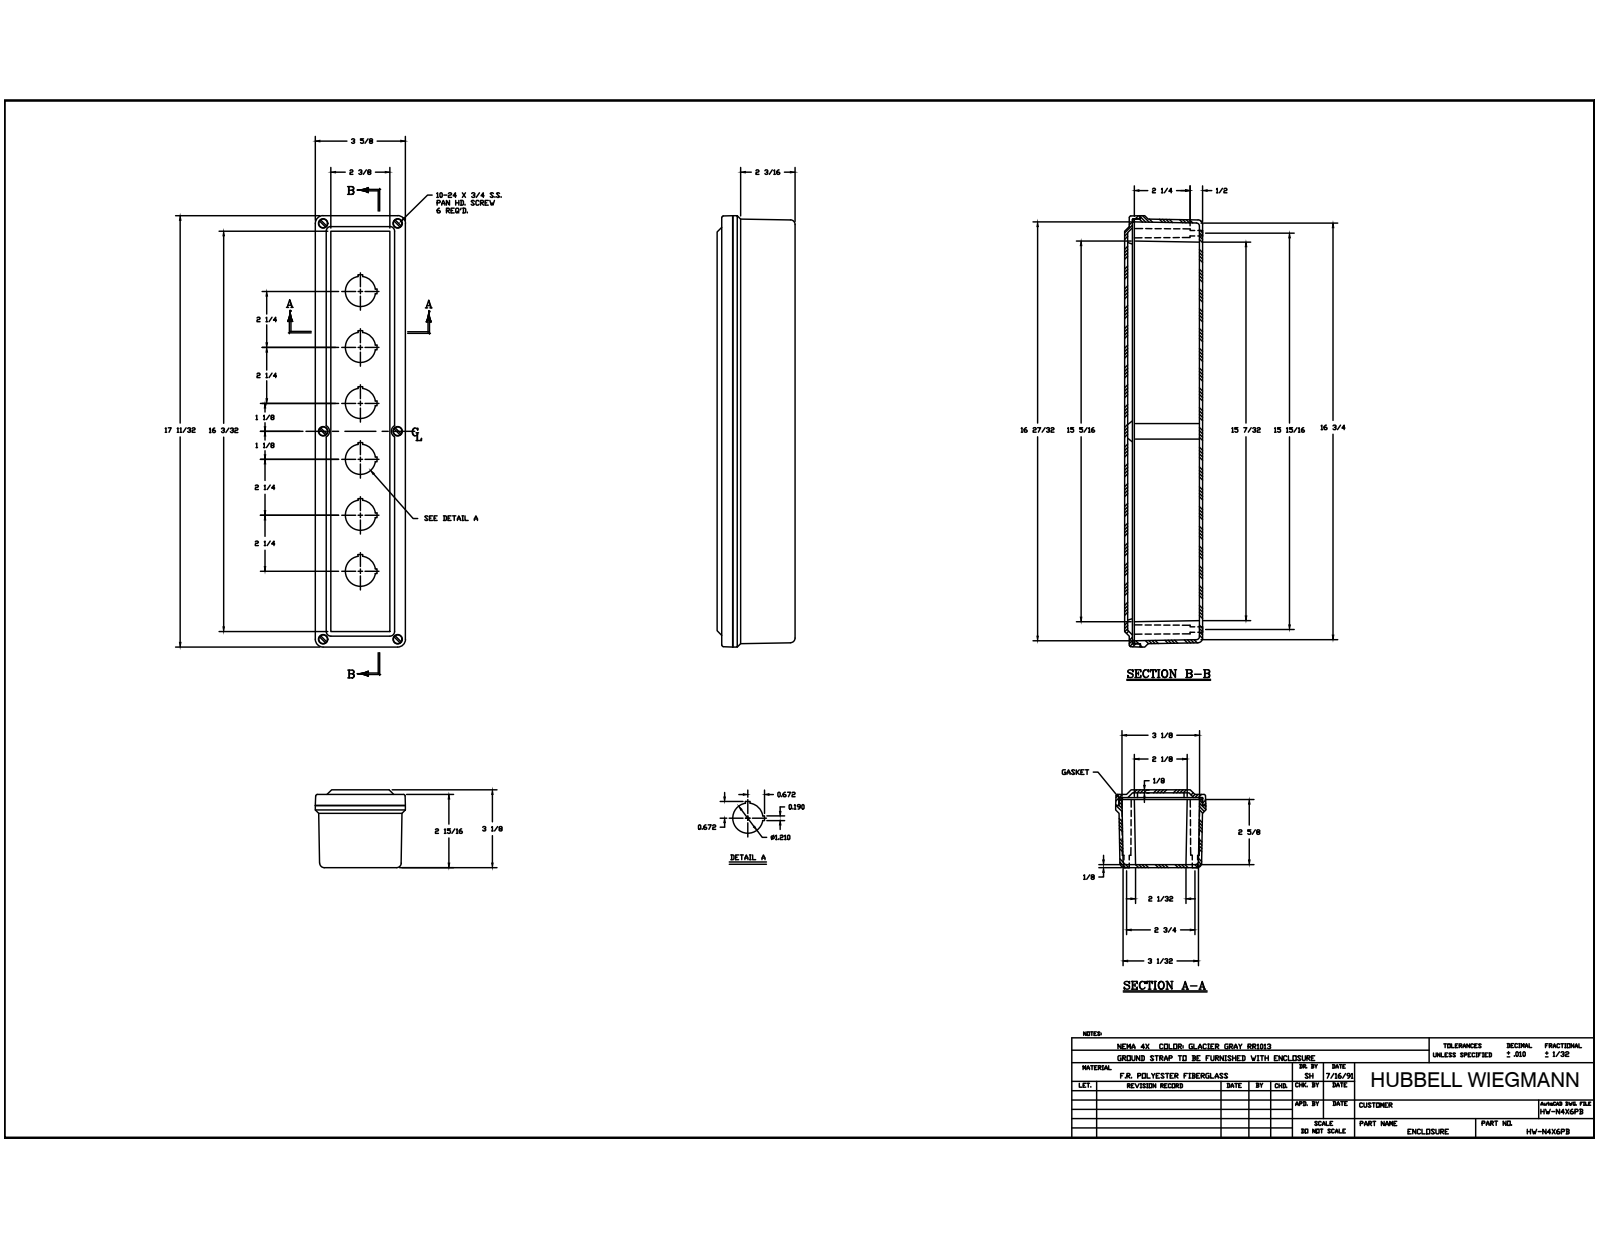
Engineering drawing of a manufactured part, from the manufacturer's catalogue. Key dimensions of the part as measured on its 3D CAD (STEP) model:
Part name (STEP PRODUCT): WPCF1732 BOX; 10-24 X 0.4375 DP BRASS INSERT; 10-24x0.75L combo screw; WPCF1732 GASKET (+3 more)
STEP written by: Autodesk Inventor 2014 (AUTOMOTIVE_DESIGN)
Units: millimetres
Bodies: 15 solids, 555 faces (265 planar, 164 cylindrical, 126 other)
Overall size (bounding box): 440.6 × 92.08 × 79.38
Volume: 564 340 mm³ · Surface area: 332 847 mm²
Round holes (diameter × count): ⌀5.56 ×8, ⌀3.68 ×6, ⌀4.83 ×6, ⌀9.52 ×6, ⌀30.73 ×6, ⌀5.5 ×2
Round bosses / shafts (diameter × count): ⌀9.42 ×6, ⌀5.54 ×6, ⌀4.5 ×6, ⌀11.18 ×2
Partial cylindrical surfaces — rounded edges, fillets, slot ends (radius × count): R0.3 ×24, R0.79 ×20, R1.22 ×8, R1.59 ×4, R4.47 ×4, R4.76 ×4, R5.59 ×4, R7.94 ×4
Main face-to-face distances: 3.17, 3.16, 76.2, 4.76, 79.37, 71.44, 73.03, 1.59, 68.27, 7.93
Hole centre spacings: 10.45, 47.62, 69.02, 73.69, 79.24, 93.81, 121.8, 132.25
